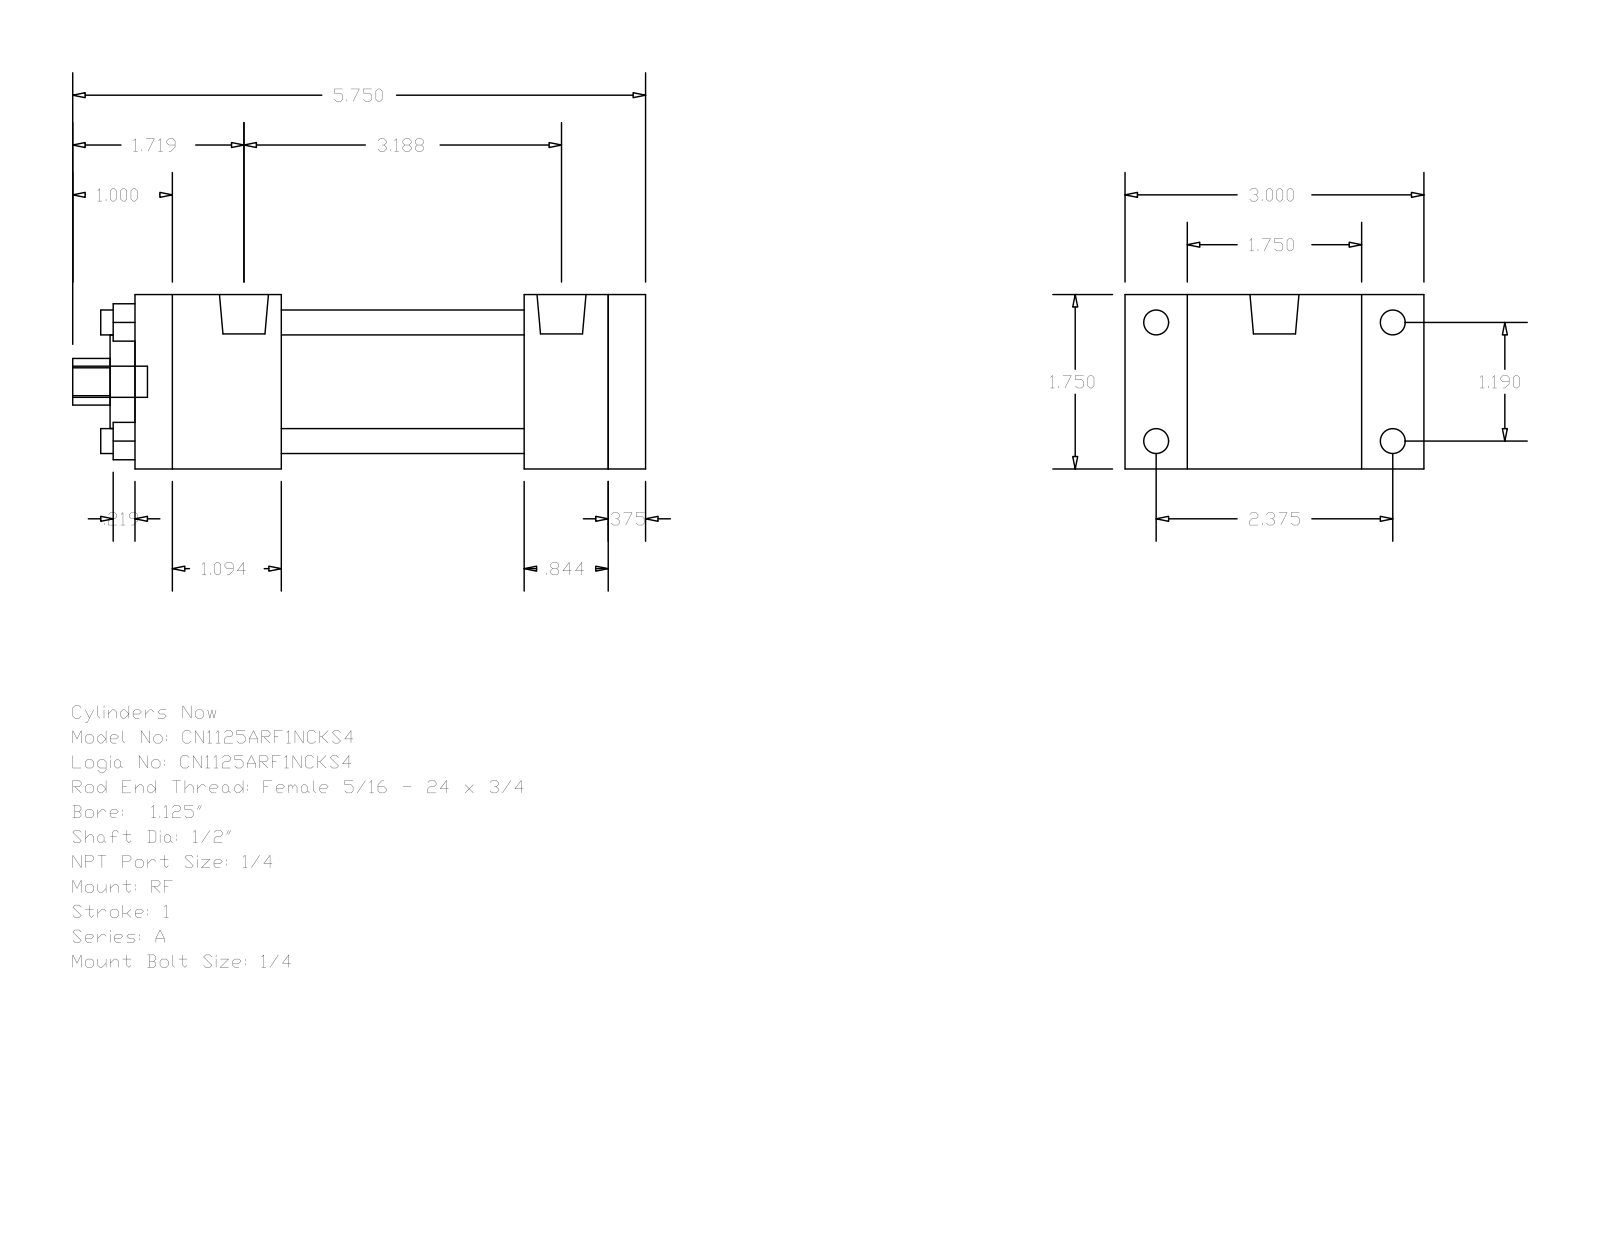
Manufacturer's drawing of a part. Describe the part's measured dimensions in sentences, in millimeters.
The part is named "A_RF__0112_0.5". Its 3-D file was written by "GSSL Pune (CONFIG_CONTROL_DESIGN)". It is 0 solids with 92 faces: 64 planar, 28 cylindrical and 0 other. Overall it measures 146.05 by 76.2 by 44.45 millimeters. Round holes: 4 of diameter 6.35, 1 of diameter 12.7, 1 of diameter 23.81, 1 of diameter 31.88. Round bosses or shafts: 4 of diameter 6.35, 4 of diameter 5.56, 2 of diameter 12.49, 1 of diameter 7.94. Partial cylindrical surfaces (rounded edges, fillets, slot ends): 1 of radius 5.94. The main face-to-face distances are 44.46, 9.52, 120.65, 130.17, 37.3, 99.21, 61.91, 83.35, 92.87, 21.44. The hole center spacings are 21.37, 30.22, 42.74.
